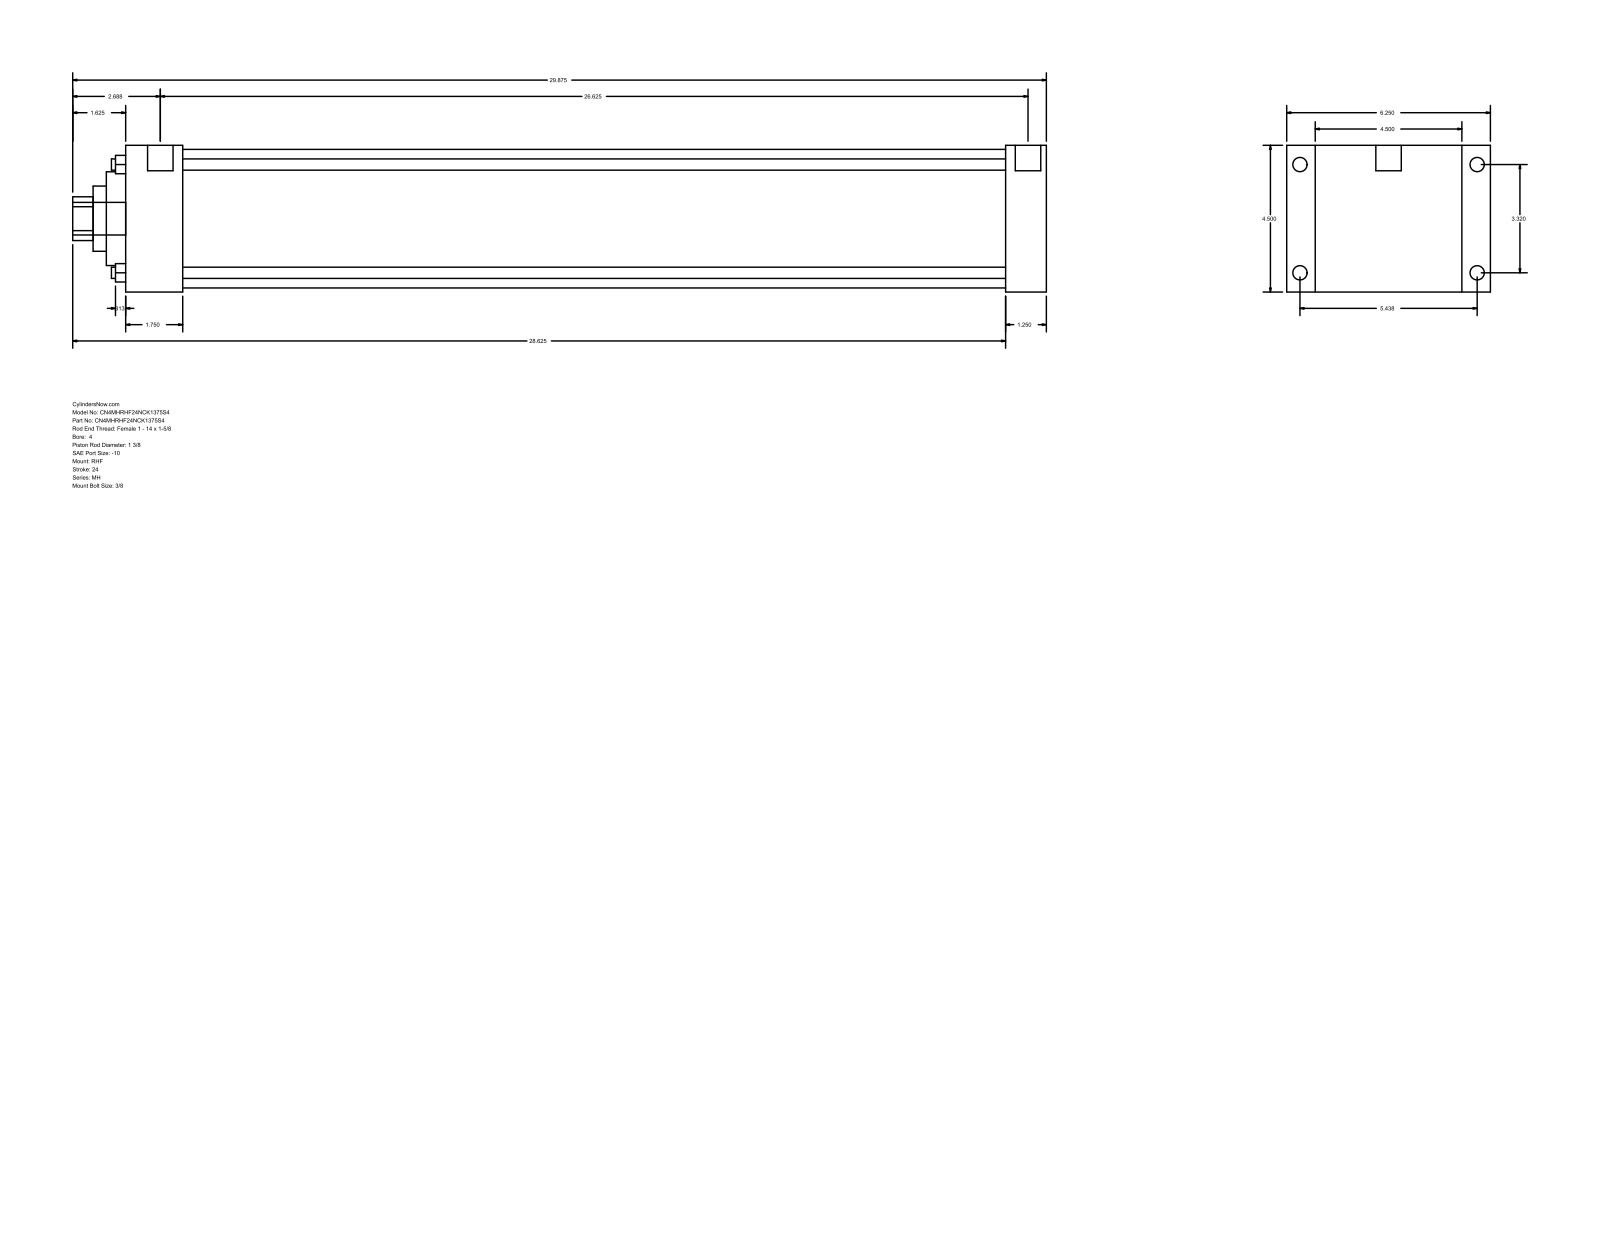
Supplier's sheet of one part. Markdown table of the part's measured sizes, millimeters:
| quantity | value |
| --- | --- |
| part name | MH_RHF__0400_1.375 |
| STEP written by | GSSL Pune (CONFIG_CONTROL_DESIGN) |
| units | millimeters |
| bodies | 0 solids, 90 faces (61 planar, 29 cylindrical, 0 other) |
| overall size | 758.83 × 158.75 × 114.3 |
| round holes (diameter × count) | 8.76 × 4, 34.92 × 1, 50.8 × 1, 73.03 × 1, 107.95 × 1 |
| round bosses / shafts (diameter × count) | 11.13 × 4, 8.73 × 4, 19.84 × 2, 25.4 × 1 |
| partial cylindrical surfaces (radius × count) | 17.06 × 1 |
| main face-to-face distances | 114.3, 717.56, 685.81, 31.75, 22.23, 136.53, 44.45, 641.36, 673.11, 158.76 |
| hole center spacings | 59.62, 84.32, 119.25 |
